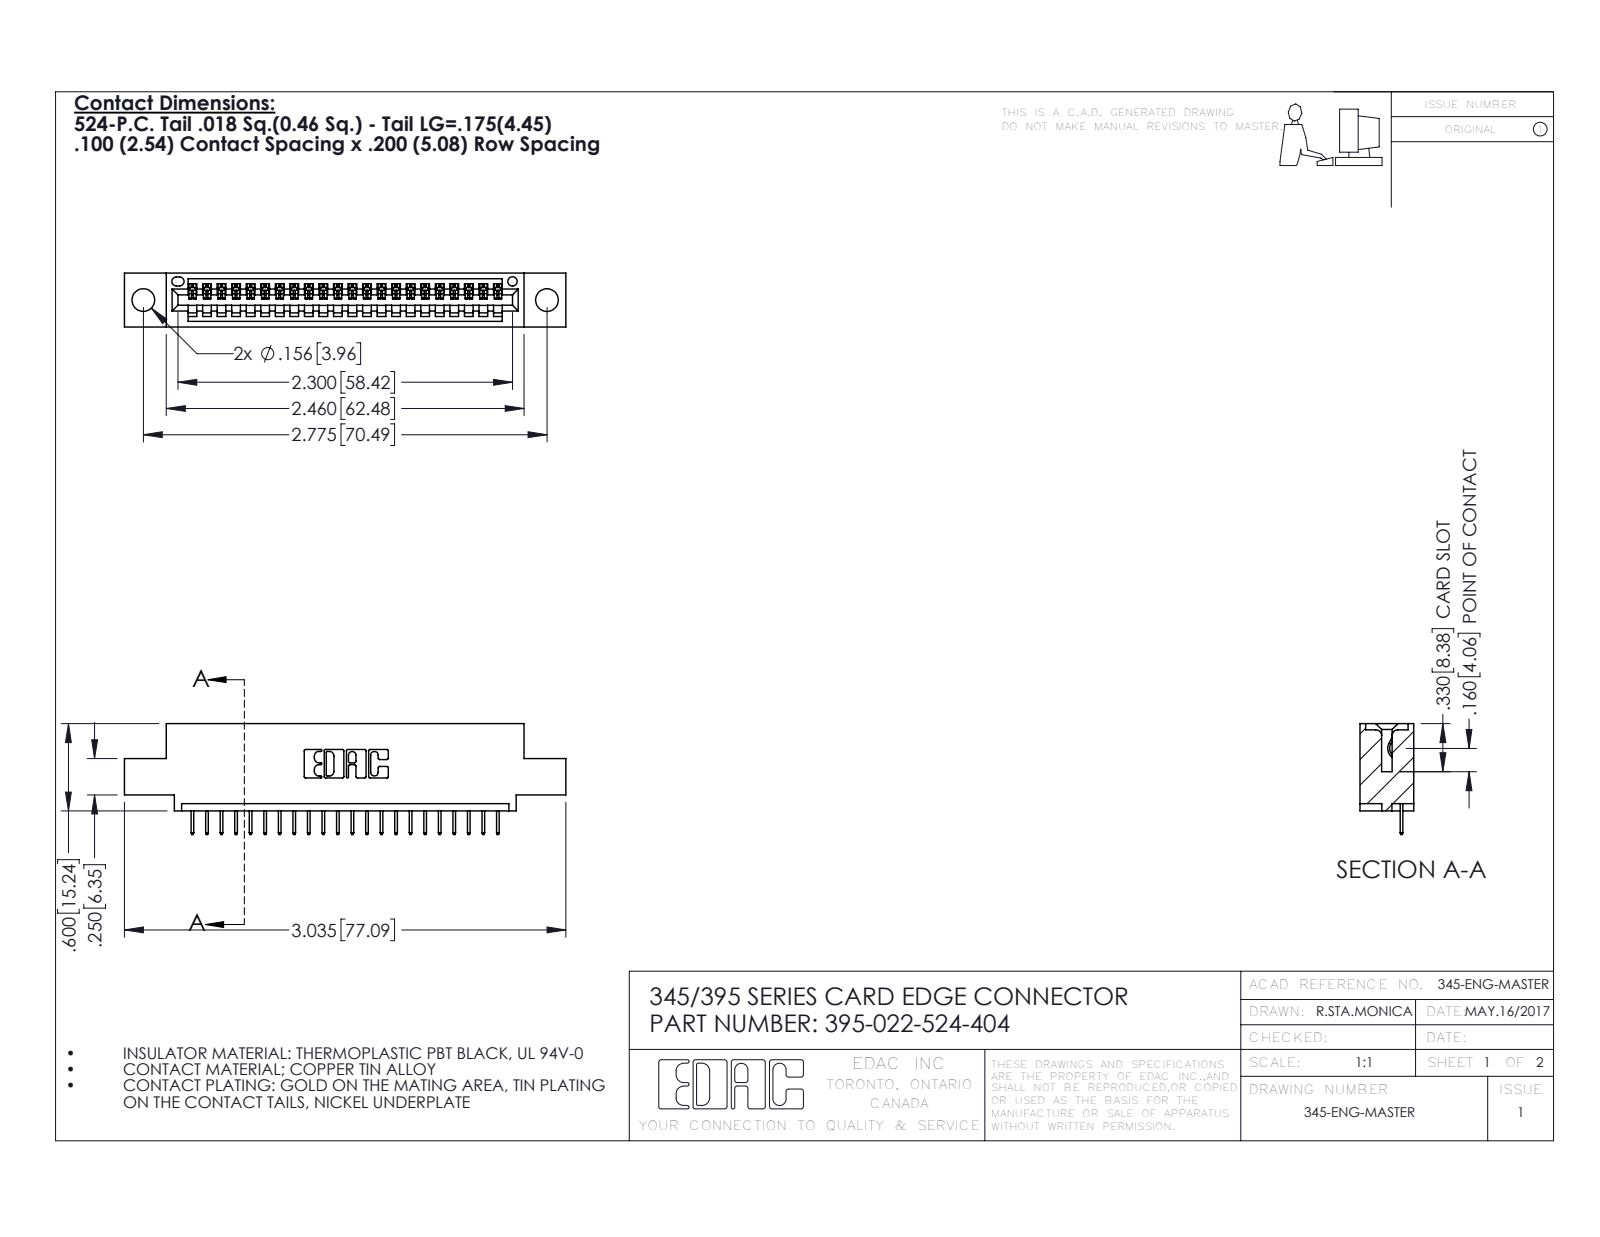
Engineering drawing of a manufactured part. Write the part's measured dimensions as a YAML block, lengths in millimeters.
part_name: "395-022-524-404; 345-292-001_345-293-124; 345 Part_0.110 Offset - 0.156 Dia-TH"
step_written_by: "SolidWorks 2016 (CONFIG_CONTROL_DESIGN)"
units: millimeters
bodies: {solids: 23, faces: 1494, planar: 1096, cylindrical: 398, other: 0}
overall_size: [77.1, 19.4, 9.4]
volume: 6920
surface_area: 8523
round_holes:
  - {diameter: 4, count: 2}
  - {diameter: 1.6, count: 1}
partial_cylinders:
  - {radius: 0.2, count: 44}
  - {radius: 0.3, count: 22}
  - {radius: 0.2, count: 6}
  - {radius: 0.8, count: 6}
  - {radius: 0.7, count: 3}
  - {radius: 0.8, count: 2}
  - {radius: 1, count: 2}
  - {radius: 0.4, count: 1}
face_to_face_distances: [1.8, 7.6, 9.4, 5.1, 2.5, 6.9, 0.6, 5.7, 1.8, 3.8]
hole_center_spacings: [6.9, 64.5, 70.5]
